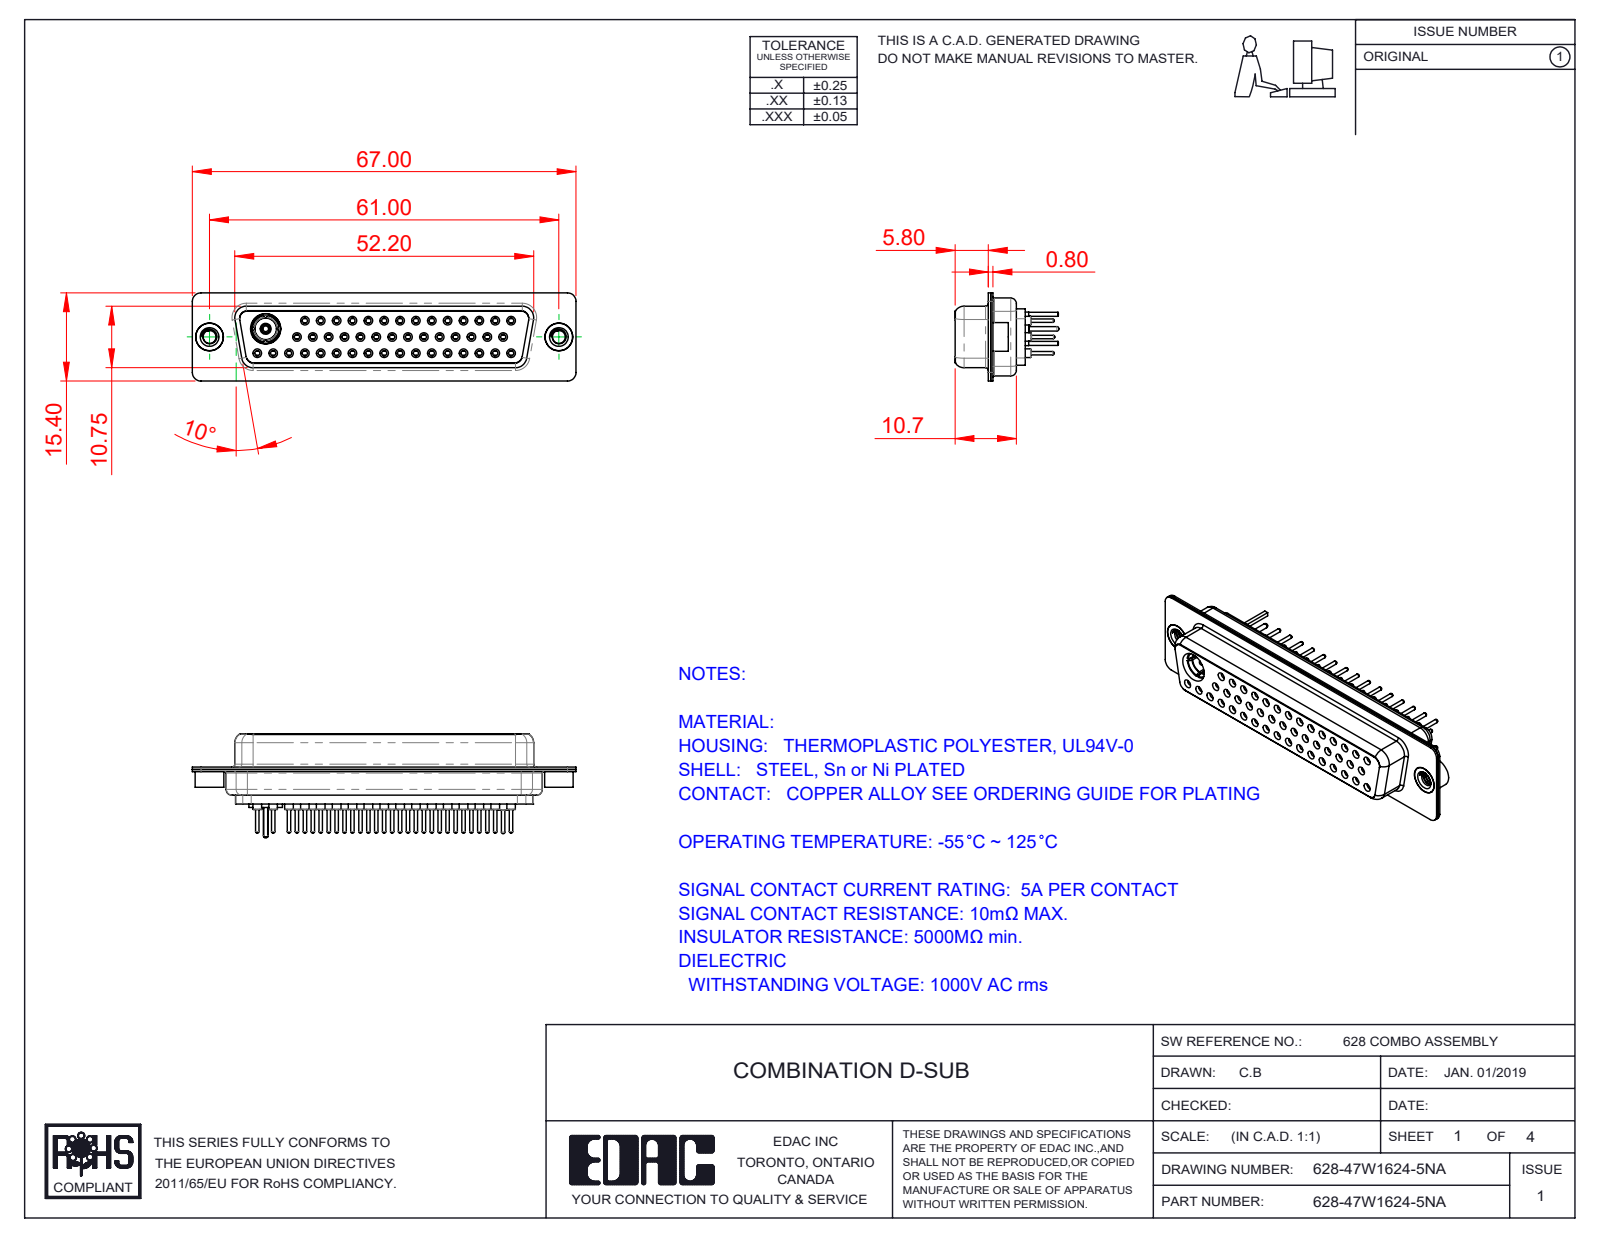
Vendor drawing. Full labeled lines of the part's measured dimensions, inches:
Part name (STEP PRODUCT): 628Combo Shell Rear_50 Contacts; 628Combo Shell Front_50 Contacts; Locking Collar; 628Combo Contact Row 1_24 (+8 more)
STEP written by: SolidWorks 2016 (CONFIG_CONTROL_DESIGN)
Units: inches
Bodies: 55 solids, 2921 faces (811 planar, 1050 cylindrical, 1060 other)
Overall size (bounding box): 2.638 × 0.715 × 0.606
Volume: 0.43 in³ · Surface area: 23.06 in²
Round holes (diameter × count): ⌀0.043 ×47, ⌀0.059 ×46, ⌀0.035 ×45, ⌀0.079 ×45, ⌀0.063 ×31, ⌀0.067 ×14, ⌀0.191 ×3, ⌀0.089 ×2, ⌀0.157 ×2, ⌀0.159 ×2, ⌀0.111 ×1, ⌀0.13 ×1
Round bosses / shafts (diameter × count): ⌀0.087 ×46, ⌀0.024 ×46, ⌀0.063 ×15, ⌀0.197 ×3, ⌀0.195 ×2, ⌀0.189 ×2, ⌀0.23 ×1, ⌀0.205 ×1
Partial cylindrical surfaces — rounded edges, fillets, slot ends (radius × count): R0.059 ×16, R0.053 ×12, R0.079 ×12, R0.063 ×8, R0.01 ×4, R0.02 ×4, R0.024 ×4, R0.026 ×4
Main face-to-face distances: 0.016, 0.238, 0.254, 0.446, 0.074, 0.482, 0.244, 0.228, 0.407, 0.43
Hole centre spacings: 0.124, 0.109, 0.218, 0.327, 0.436, 0.545, 0.654, 0.763
